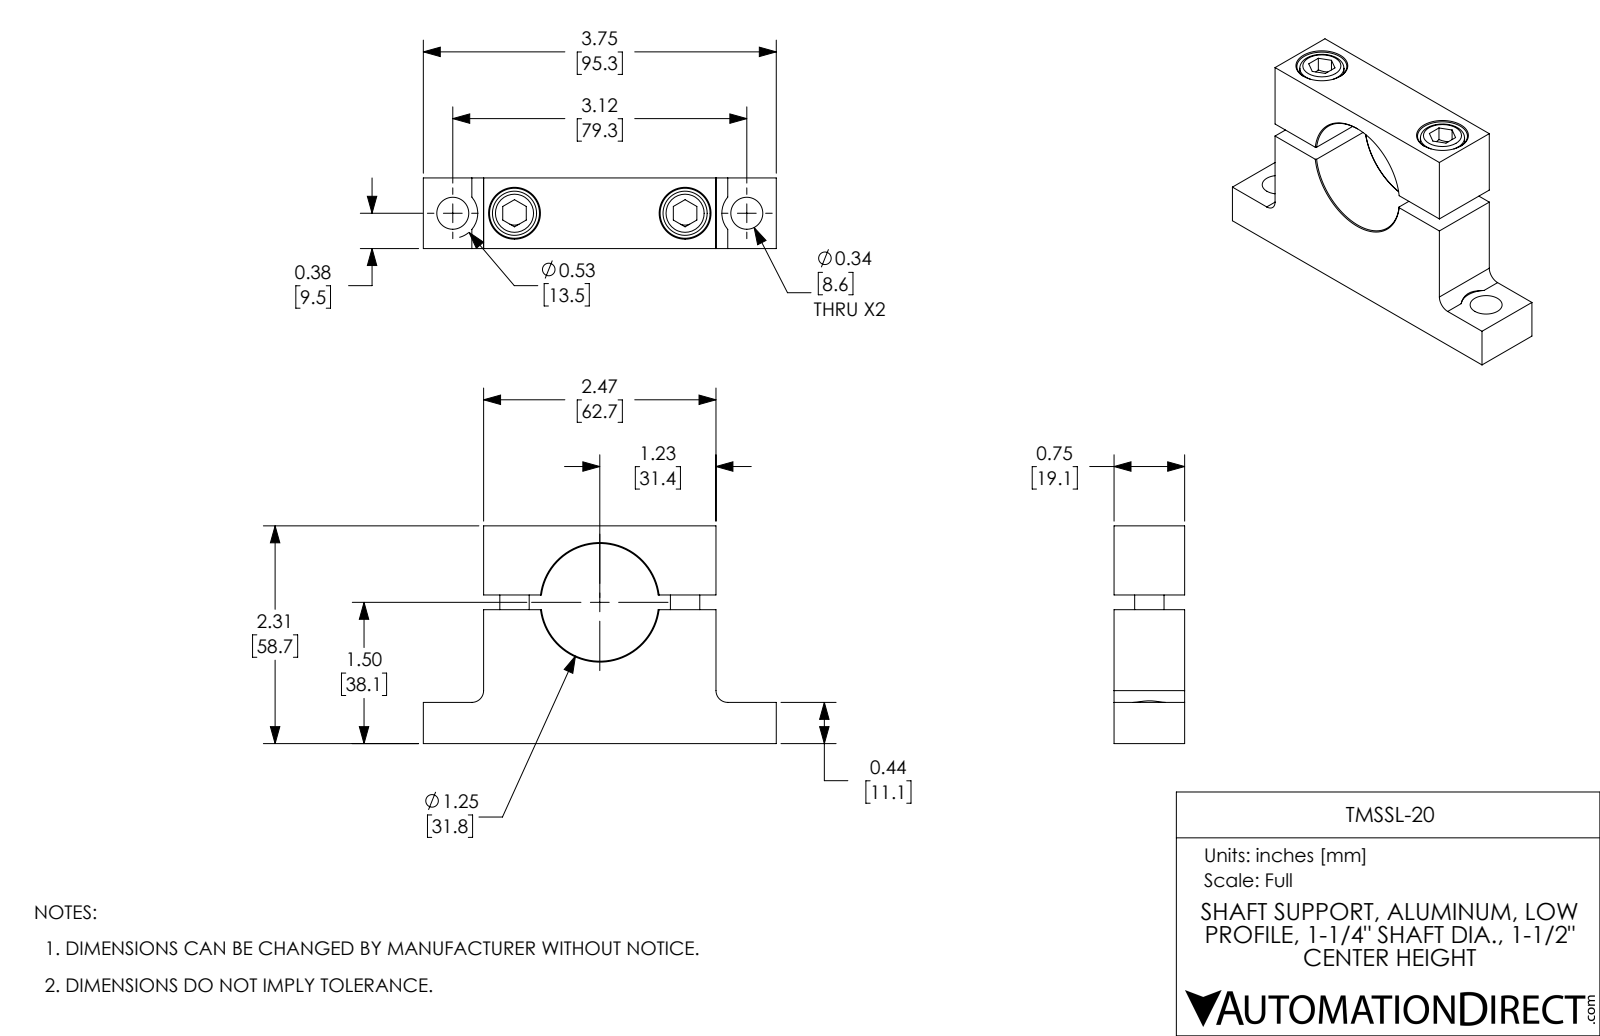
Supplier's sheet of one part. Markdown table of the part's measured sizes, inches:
| quantity | value |
| --- | --- |
| part name | TMSSL-20 |
| STEP written by | SolidWorks 2017 (AUTOMOTIVE_DESIGN) |
| units | inches |
| bodies | 4 solids, 92 faces (38 planar, 30 cylindrical, 24 other) |
| overall size | 3.75 × 2.312 × 0.75 |
| volume | 3.487 in³ |
| surface area | 31.45 in² |
| round holes (diameter × count) | 0.252 × 2, 0.332 × 2, 0.34 × 2, 0.531 × 2, 1.25 × 1 |
| round bosses / shafts (diameter × count) | 0.469 × 2, 0.312 × 2 |
| partial cylindrical surfaces (radius × count) | 0.125 × 2, 0.266 × 2 |
| main face-to-face distances | 0.75, 2.312, 2.469, 1.422, 0.89, 1.578, 0.156, 0.734, 0.641, 0.641 |
| hole center spacings | 0.656, 2.468, 1.813, 3.124 |
